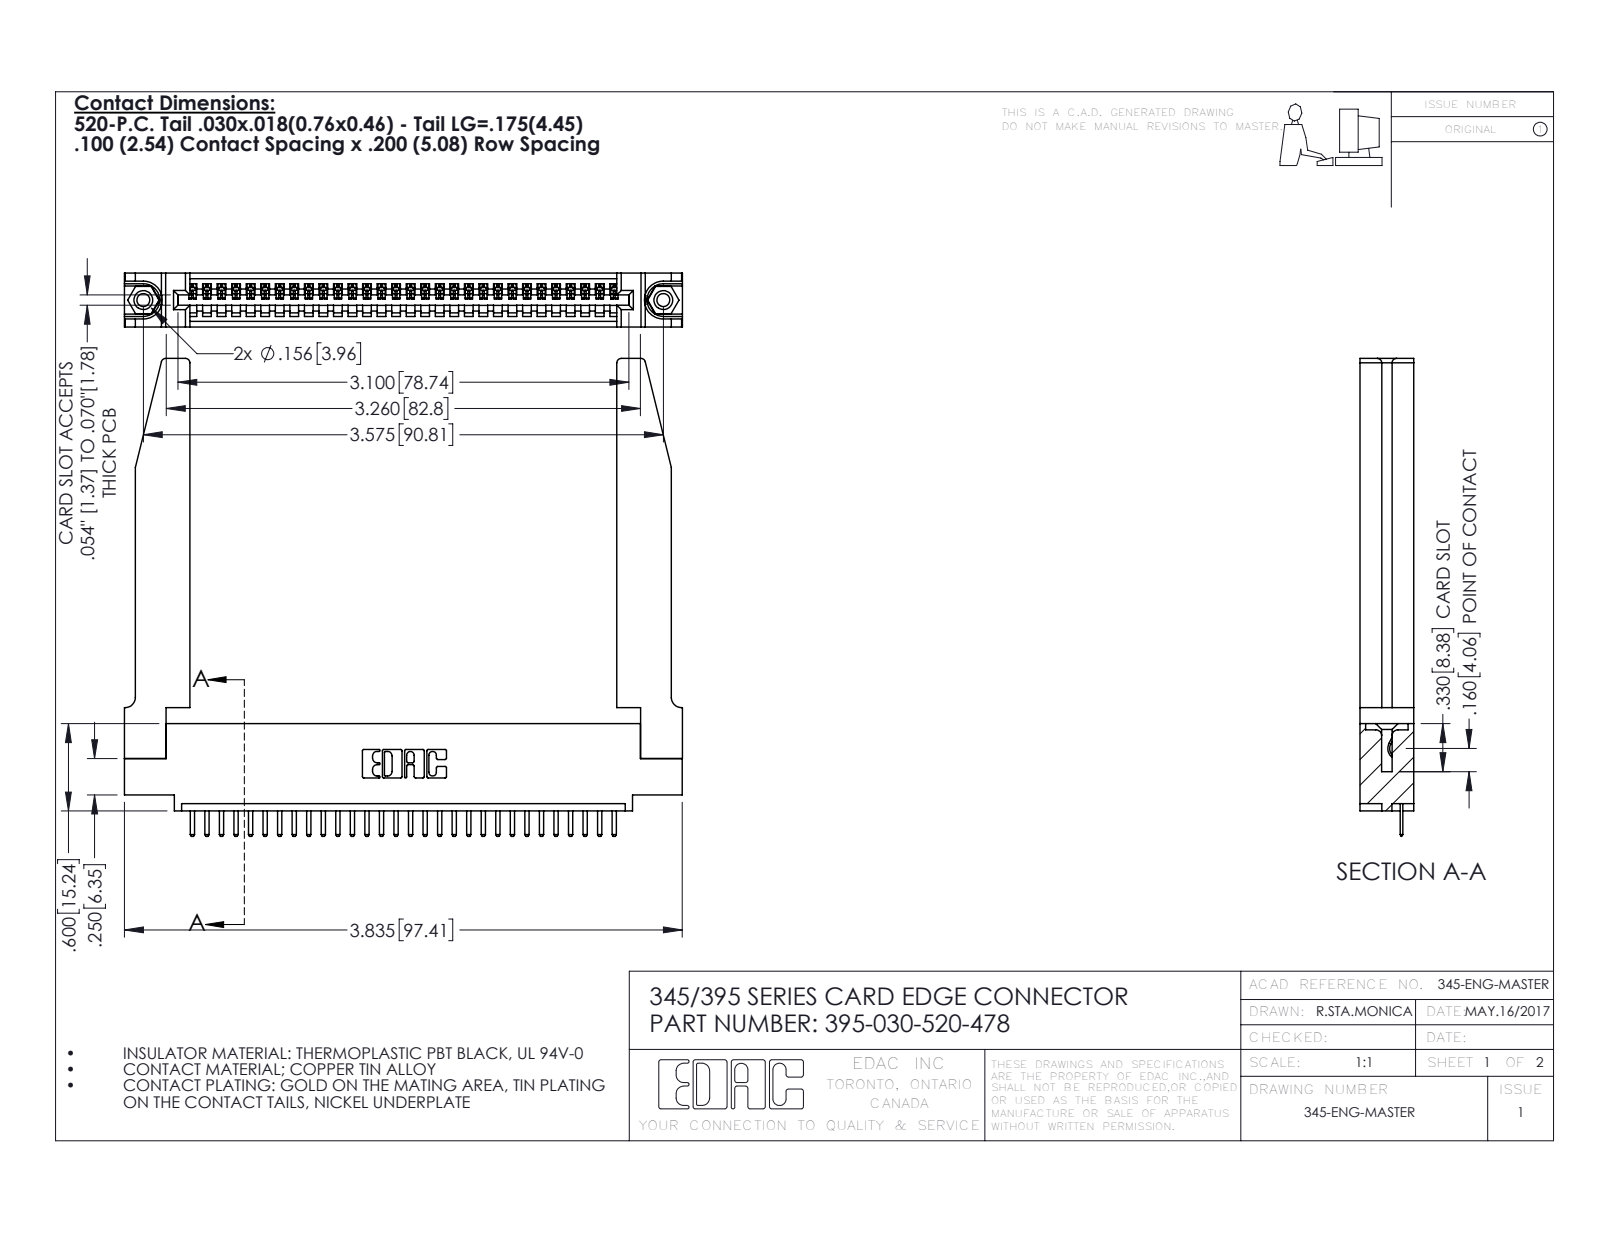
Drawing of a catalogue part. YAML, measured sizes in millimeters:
part_name: "395-030-520-478; 345 Part_0.110 Offset - 0.156 Dia-TH; 345-250-001_345-250-001-102; 345-292-001_345-293-120 (+1 more)"
step_written_by: "SolidWorks 2016 (CONFIG_CONTROL_DESIGN)"
units: millimeters
bodies: {solids: 35, faces: 2224, planar: 1486, cylindrical: 686, other: 52}
overall_size: [97.4, 83.4, 9.4]
volume: 16760
surface_area: 18440
round_holes:
  - {diameter: 2.3, count: 2}
  - {diameter: 3.2, count: 2}
  - {diameter: 4, count: 2}
  - {diameter: 1.6, count: 1}
round_bosses_or_shafts:
  - {diameter: 3.9, count: 2}
partial_cylinders:
  - {radius: 0.3, count: 62}
  - {radius: 0.2, count: 60}
  - {radius: 0.3, count: 22}
  - {radius: 0.8, count: 8}
  - {radius: 0.2, count: 6}
  - {radius: 0.8, count: 6}
  - {radius: 0.7, count: 3}
  - {radius: 0.8, count: 2}
face_to_face_distances: [9.4, 1.8, 7.6, 5.1, 2.5, 6.9, 0.6, 3.8, 3.8, 5.7]
hole_center_spacings: [6.9, 84.8, 90.8]
